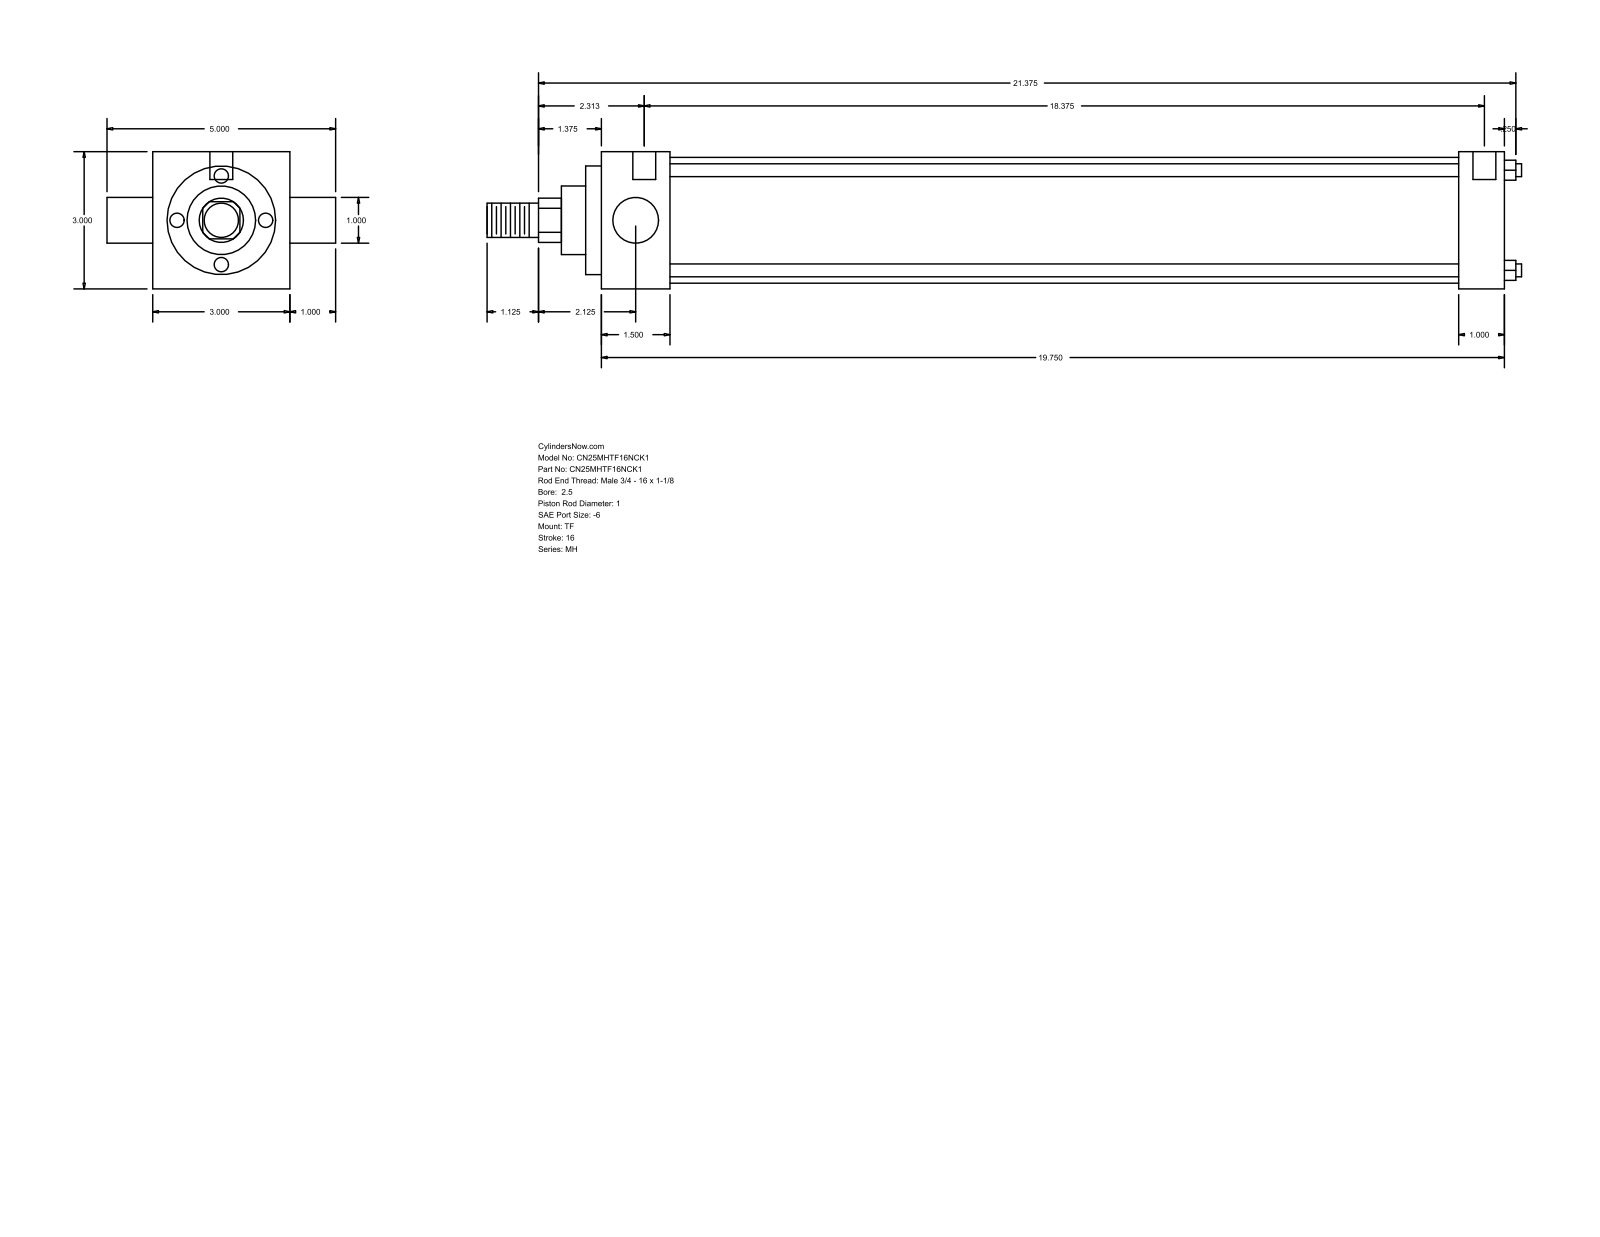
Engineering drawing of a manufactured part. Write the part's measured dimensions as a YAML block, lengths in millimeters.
part_name: "MH_TF__0250_1"
step_written_by: "GSSL Pune (CONFIG_CONTROL_DESIGN)"
units: millimeters
bodies: {solids: 0, faces: 86, planar: 61, cylindrical: 25, other: 0}
overall_size: [574.67, 127, 76.2]
round_holes:
  - {diameter: 5.56, count: 3}
  - {diameter: 12.7, count: 2}
round_bosses_or_shafts:
  - {diameter: 7.14, count: 4}
  - {diameter: 25.4, count: 2}
  - {diameter: 69.85, count: 1}
  - {diameter: 60.33, count: 1}
  - {diameter: 38.1, count: 1}
  - {diameter: 19.05, count: 1}
partial_cylinders:
  - {radius: 12.29, count: 1}
face_to_face_distances: [76.2, 501.66, 25.4, 38.11, 463.55, 476.26, 438.15, 8.73, 46.84, 484.99]
hole_center_spacings: [3.18, 4.76, 466.72, 469.9, 471.48, 474.66]
